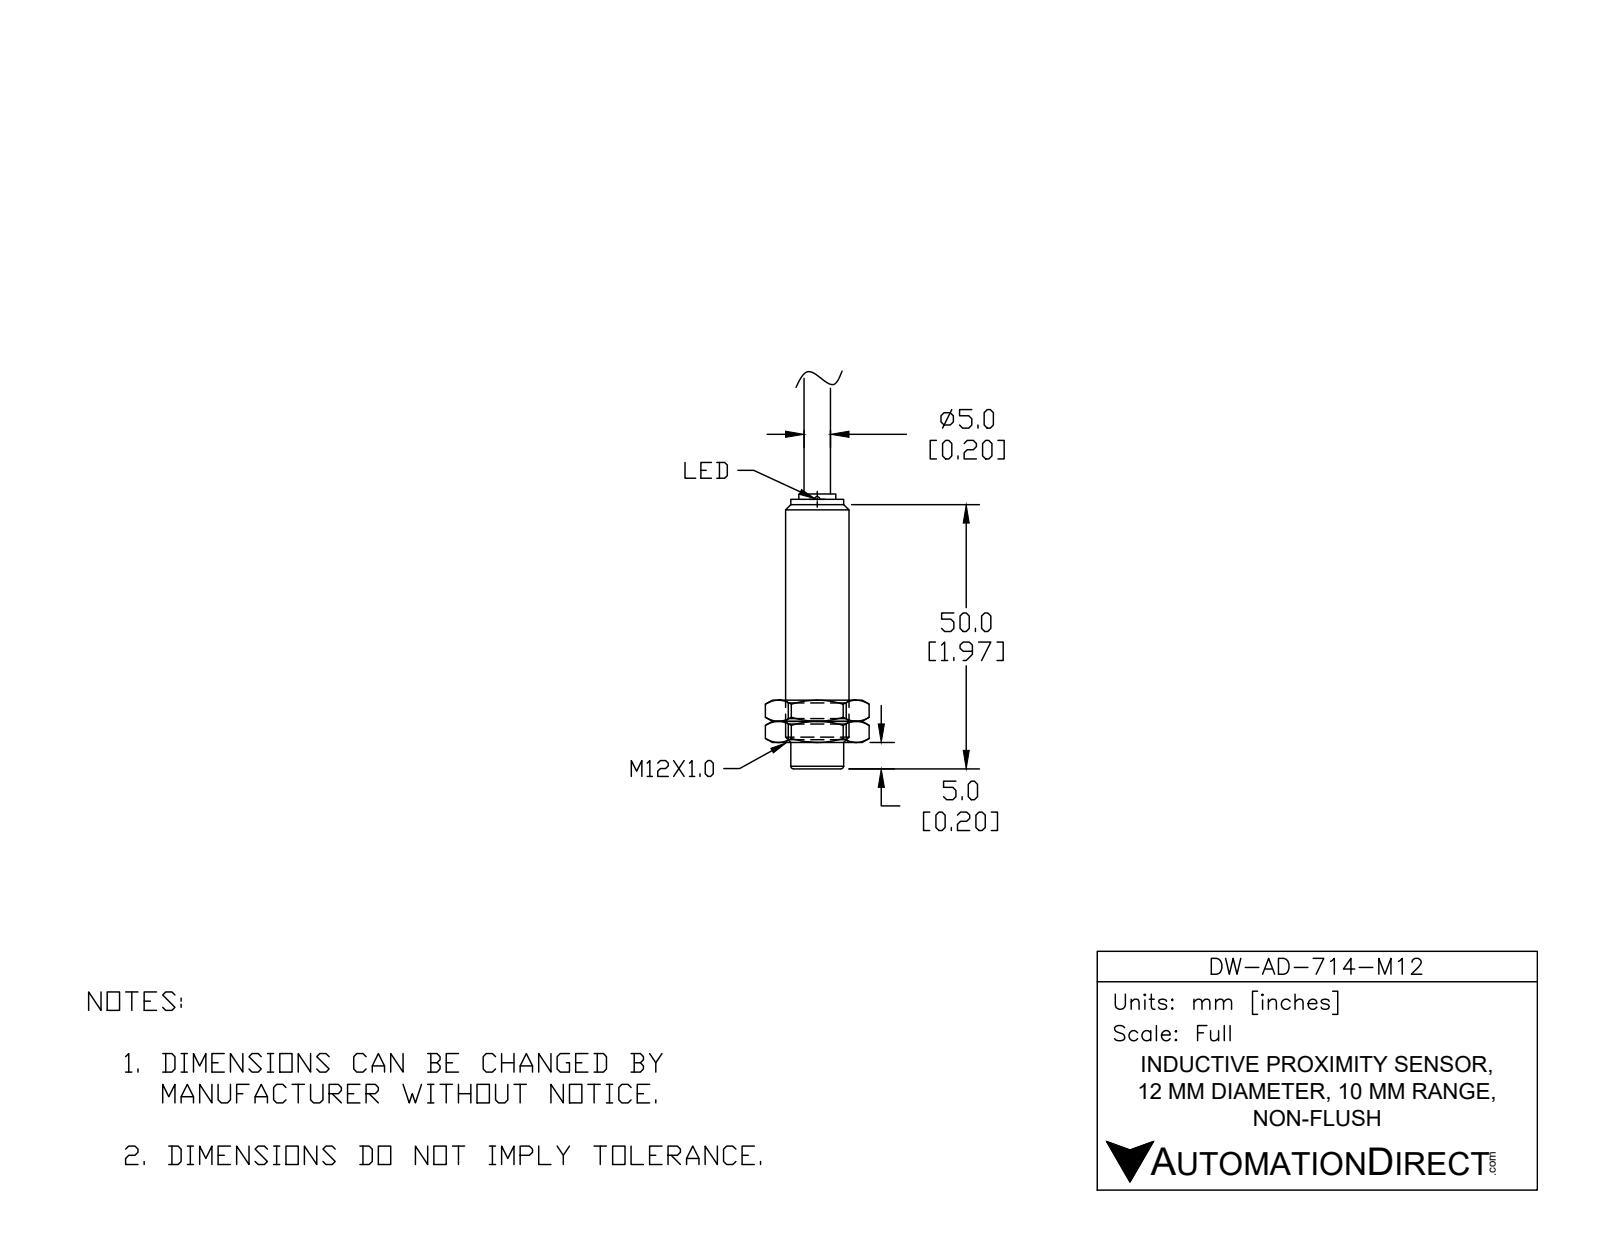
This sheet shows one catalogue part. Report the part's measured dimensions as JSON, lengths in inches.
{"part_name": "DW-AD-714-M12", "step_written_by": "SolidWorks 2017 (AUTOMOTIVE_DESIGN)", "units": "inches", "bodies": {"solids": 2, "faces": 34, "planar": 17, "cylindrical": 6, "other": 11}, "overall_size": [2.976, 0.472, 0.472], "volume_in3": 0.377, "surface_area_in2": 4.017, "round_bosses_or_shafts": [[0.472, 1], [0.415, 1], [0.413, 1], [0.268, 1], [0.197, 1], [0.118, 1]], "face_to_face_distances": [2.047, 2, 0.047, 1.85, 0.15, 0.197, 2.031, 0.181, 0.031, 0.016]}
